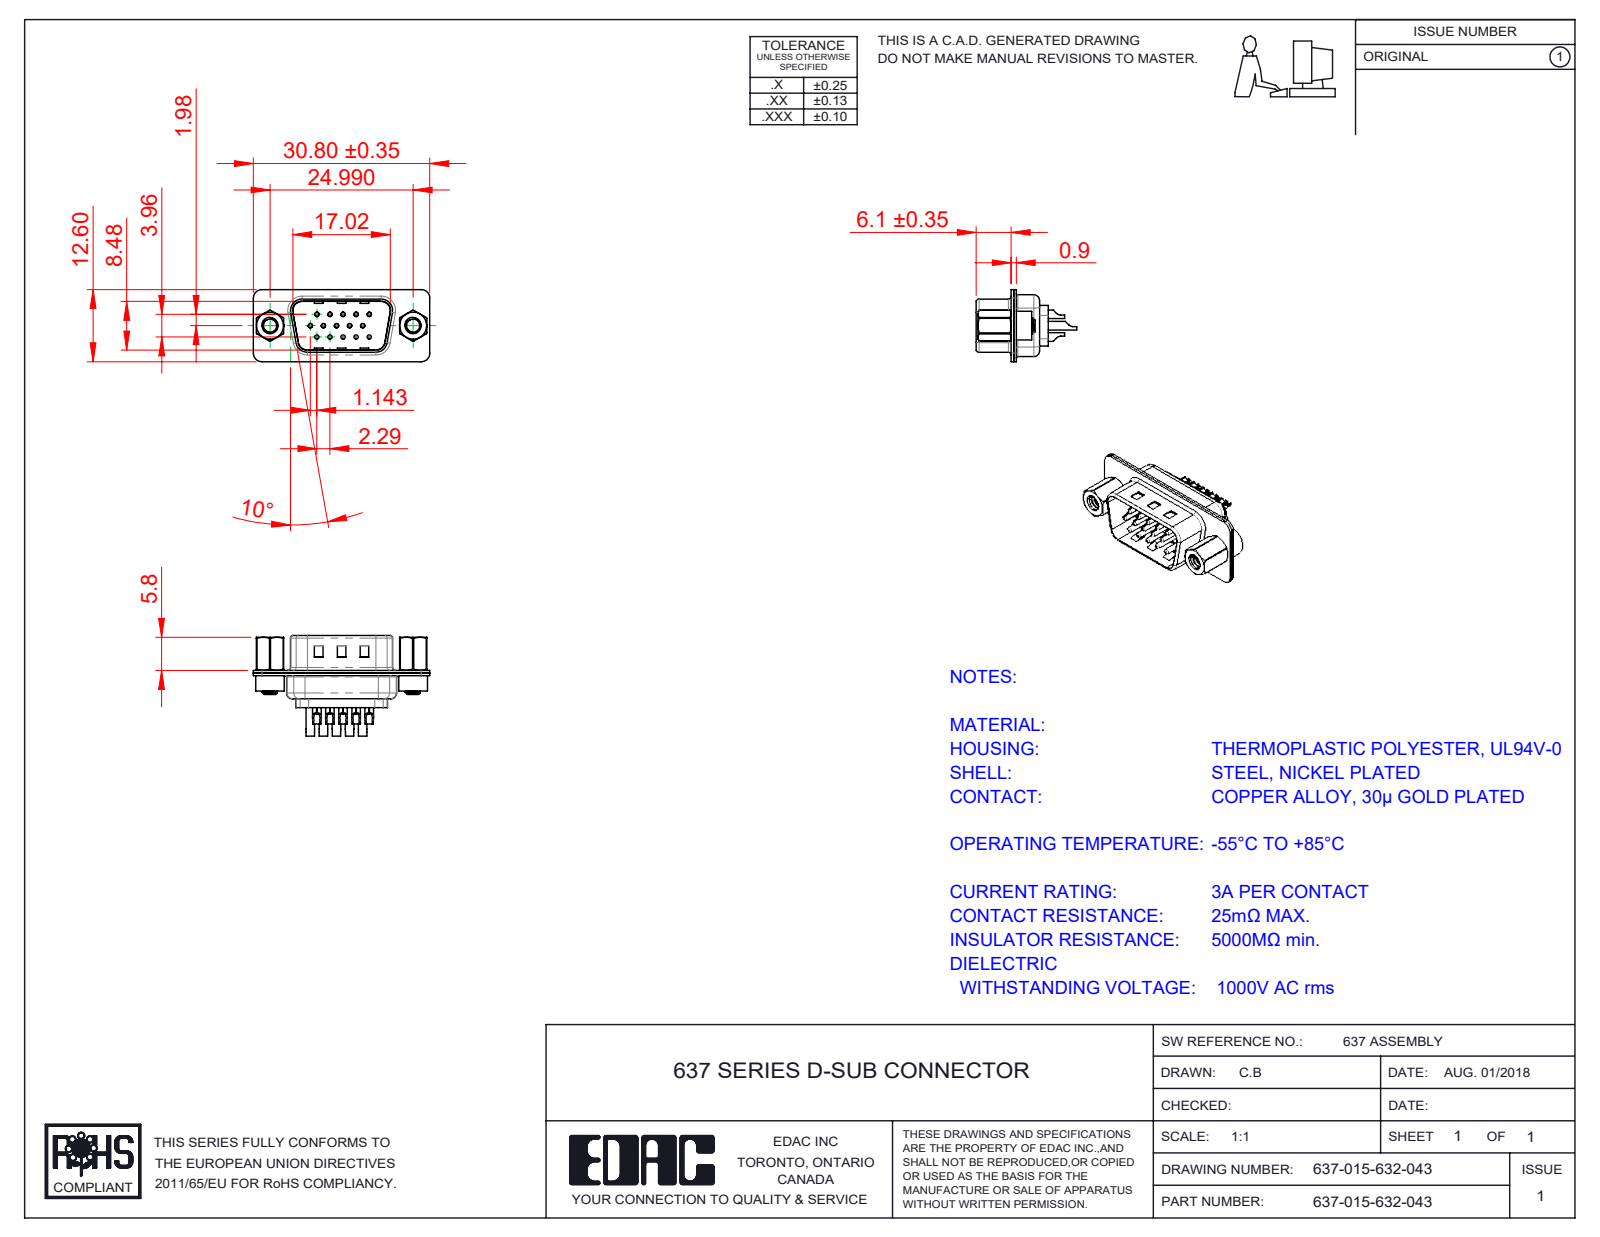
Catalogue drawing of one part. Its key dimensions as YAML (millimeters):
part_name: "637 Housing_15 Contacts; 637 4-40 Threaded Rivet; 637 Contact Row 1_32; 637 Shell Front_15 Contacts (+5 more)"
step_written_by: "SolidWorks 2020 (CONFIG_CONTROL_DESIGN)"
units: millimeters
bodies: {solids: 22, faces: 1390, planar: 339, cylindrical: 636, other: 415}
overall_size: [30.8, 17.55, 12.6]
volume: 1544
surface_area: 5262
round_holes:
  - {diameter: 0.35, count: 15}
  - {diameter: 1.1, count: 15}
  - {diameter: 1.6, count: 15}
  - {diameter: 2.26, count: 2}
  - {diameter: 2.29, count: 2}
  - {diameter: 4, count: 2}
  - {diameter: 4.8, count: 2}
round_bosses_or_shafts:
  - {diameter: 2, count: 15}
  - {diameter: 1.5, count: 15}
  - {diameter: 0.75, count: 15}
  - {diameter: 5, count: 2}
  - {diameter: 4.9, count: 2}
  - {diameter: 2.79, count: 2}
partial_cylinders:
  - {radius: 1.5, count: 16}
  - {radius: 2, count: 12}
  - {radius: 0.5, count: 8}
  - {radius: 1, count: 7}
  - {radius: 0.25, count: 4}
  - {radius: 0.55, count: 4}
  - {radius: 0.7, count: 4}
  - {radius: 0.95, count: 4}
face_to_face_distances: [0.45, 0.9, 0.4, 0.7, 8.88, 8.48, 1.05, 0.31, 4.55, 6.5]
hole_center_spacings: [3.96, 2.28, 4.57, 2.29, 6.05, 6.86, 7.92, 6.04]
